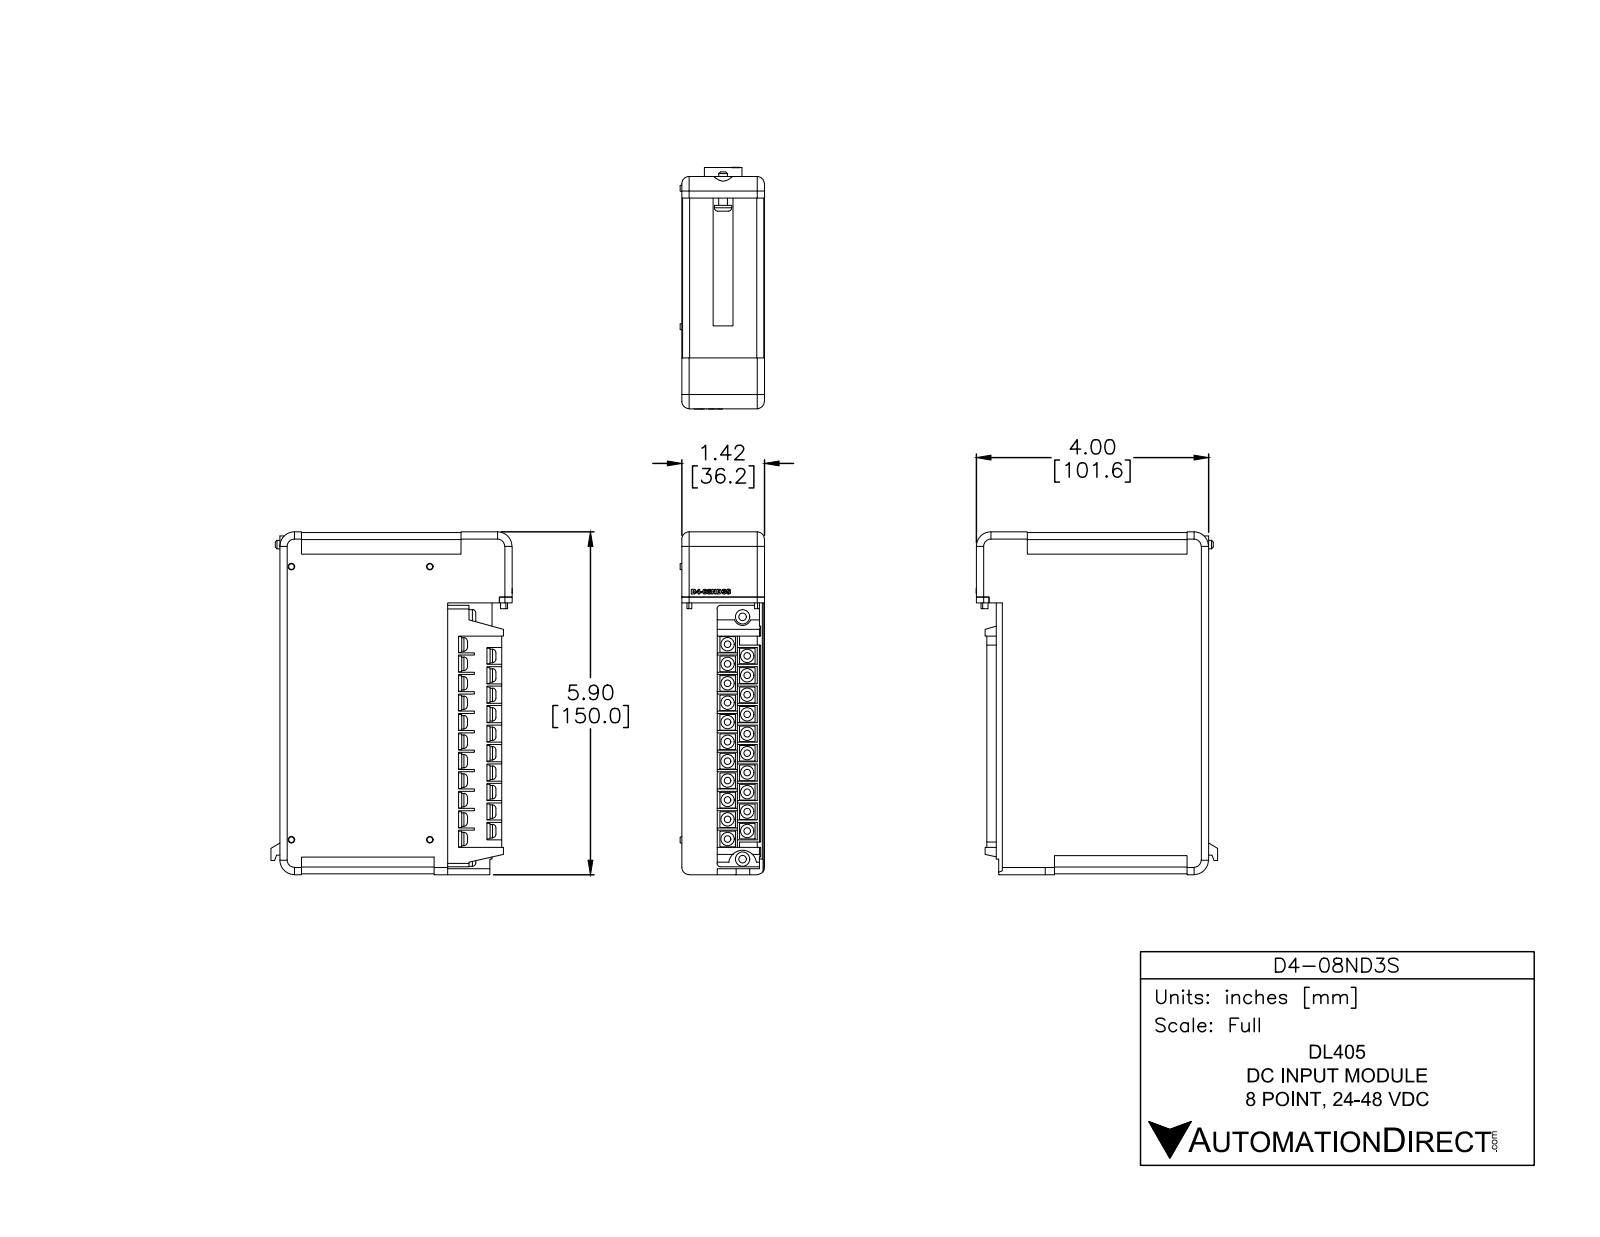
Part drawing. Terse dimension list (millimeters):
name: D4-08ND3S
written by: SolidWorks 2014 (AUTOMOTIVE_DESIGN)
unit: mm
bodies: 15 solids, 631 faces (412 planar, 86 cylindrical, 133 other)
size: 150 × 105.6 × 37
volume: 450 800 mm³; area: 56 030 mm²
bosses: 21× ⌀5.8, 2× ⌀6.4, 1× ⌀7.6, 1× ⌀3.8
rounds: 8× R3.2, 4× R3, 3× R6.4, 2× R0.4, 2× R0.8, 2× R1.5, 1× R3.8, 1× R3.8
face distances: 36.2, 0.4, 73.4, 149.2, 35.8, 11.9, 5.1, 24.3, 149.6, 30.7
